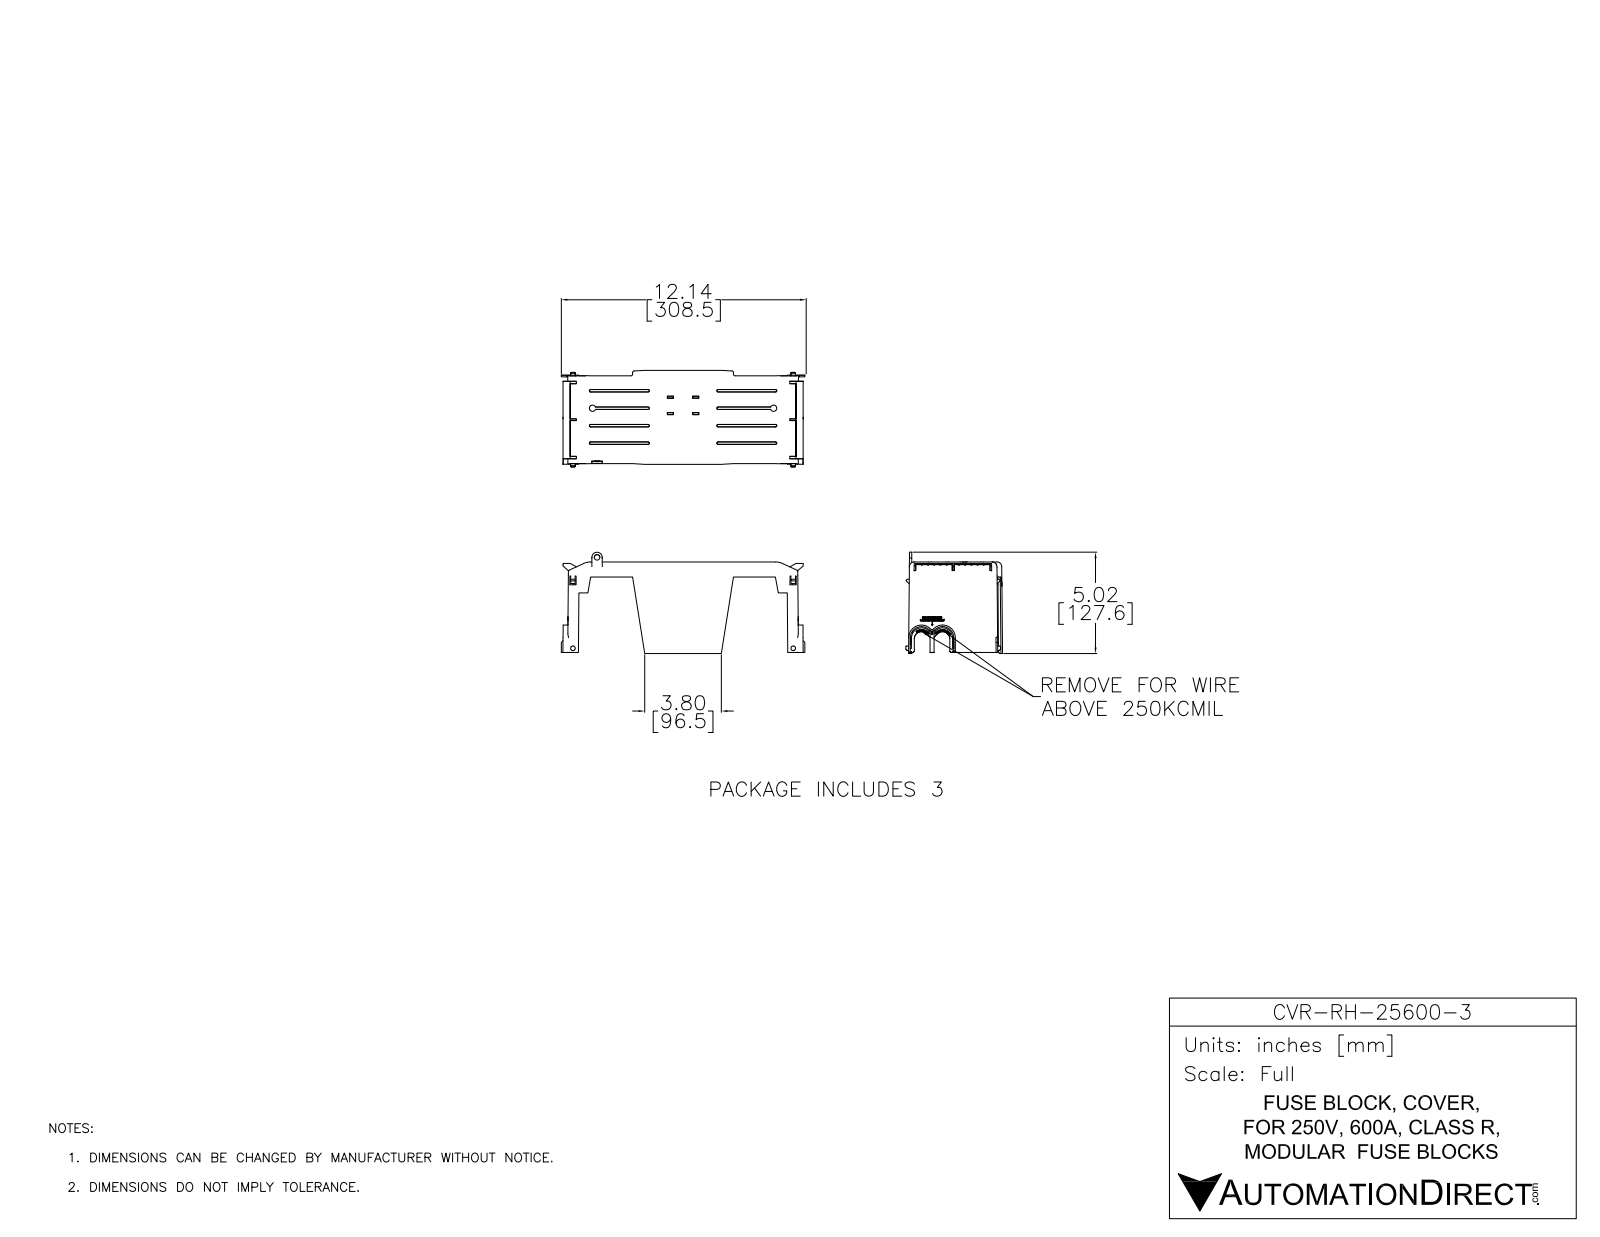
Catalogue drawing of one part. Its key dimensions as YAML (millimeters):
part_name: "CVR-RH-25600-3"
step_written_by: "SolidWorks 2017 (AUTOMOTIVE_DESIGN)"
units: millimeters
bodies: {solids: 1, faces: 2344, planar: 1576, cylindrical: 119, other: 649}
overall_size: [306.7, 127.7, 121.8]
volume: 211900
surface_area: 215100
round_holes:
  - {diameter: 7, count: 1}
partial_cylinders:
  - {radius: 1, count: 18}
  - {radius: 4, count: 9}
  - {radius: 3, count: 8}
  - {radius: 6, count: 7}
  - {radius: 2, count: 4}
  - {radius: 9, count: 4}
  - {radius: 12.5, count: 4}
  - {radius: 14, count: 4}
face_to_face_distances: [2, 6, 4, 8, 5, 3, 20.2, 64, 4, 22]
